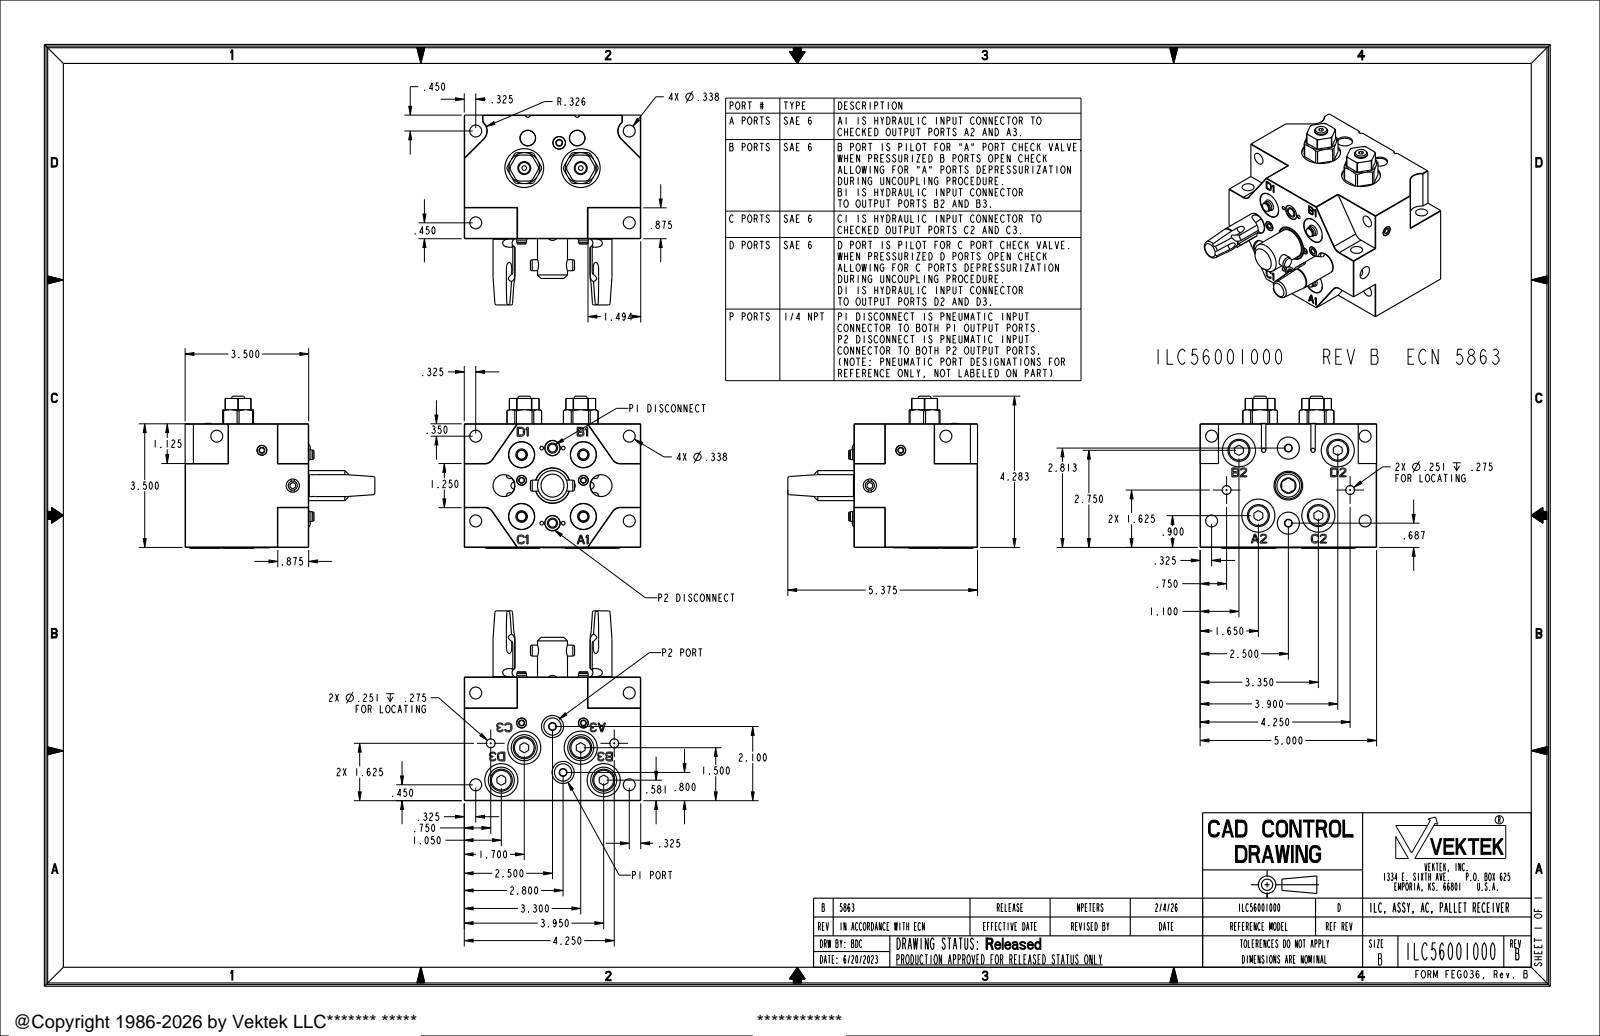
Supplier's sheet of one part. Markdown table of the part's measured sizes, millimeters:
| quantity | value |
| --- | --- |
| part name | ILC56001000 |
| STEP written by | CREO PARAMETRIC BY PTC INC, 2021164 (AUTOMOTIVE_DESIGN) |
| units | millimeters |
| bodies | 9 solids, 2480 faces (1617 planar, 317 cylindrical, 546 other) |
| overall size | 136.5 × 127 × 109.5 |
| volume | 911 600 mm³ |
| surface area | 108 900 mm² |
| round holes (diameter × count) | 8.6 × 8, 23.8 × 8, 3.6 × 5, 4.2 × 5, 7.1 × 5, 2.6 × 4, 15.9 × 4, 3 × 2, 8.4 × 2, 11.2 × 2, 15.7 × 2, 27.9 × 2 |
| round bosses / shafts (diameter × count) | 7 × 9, 6.3 × 9, 15.7 × 2, 15.6 × 2, 11.1 × 2, 7.2 × 2, 25.3 × 1, 21.6 × 1 |
| partial cylindrical surfaces (radius × count) | 2.4 × 6, 3.2 × 5, 2.4 × 4, 6.5 × 4, 1.6 × 2, 8 × 2, 10.3 × 2, 10.7 × 2 |
| main face-to-face distances | 88.9, 127, 22.2, 66.7, 1.9, 87, 28.6, 60.3, 92.6, 58.4 |
| hole center spacings | 7.7, 25.4, 28.1, 38.3, 44.1, 50.5, 53.3, 54.6 |
